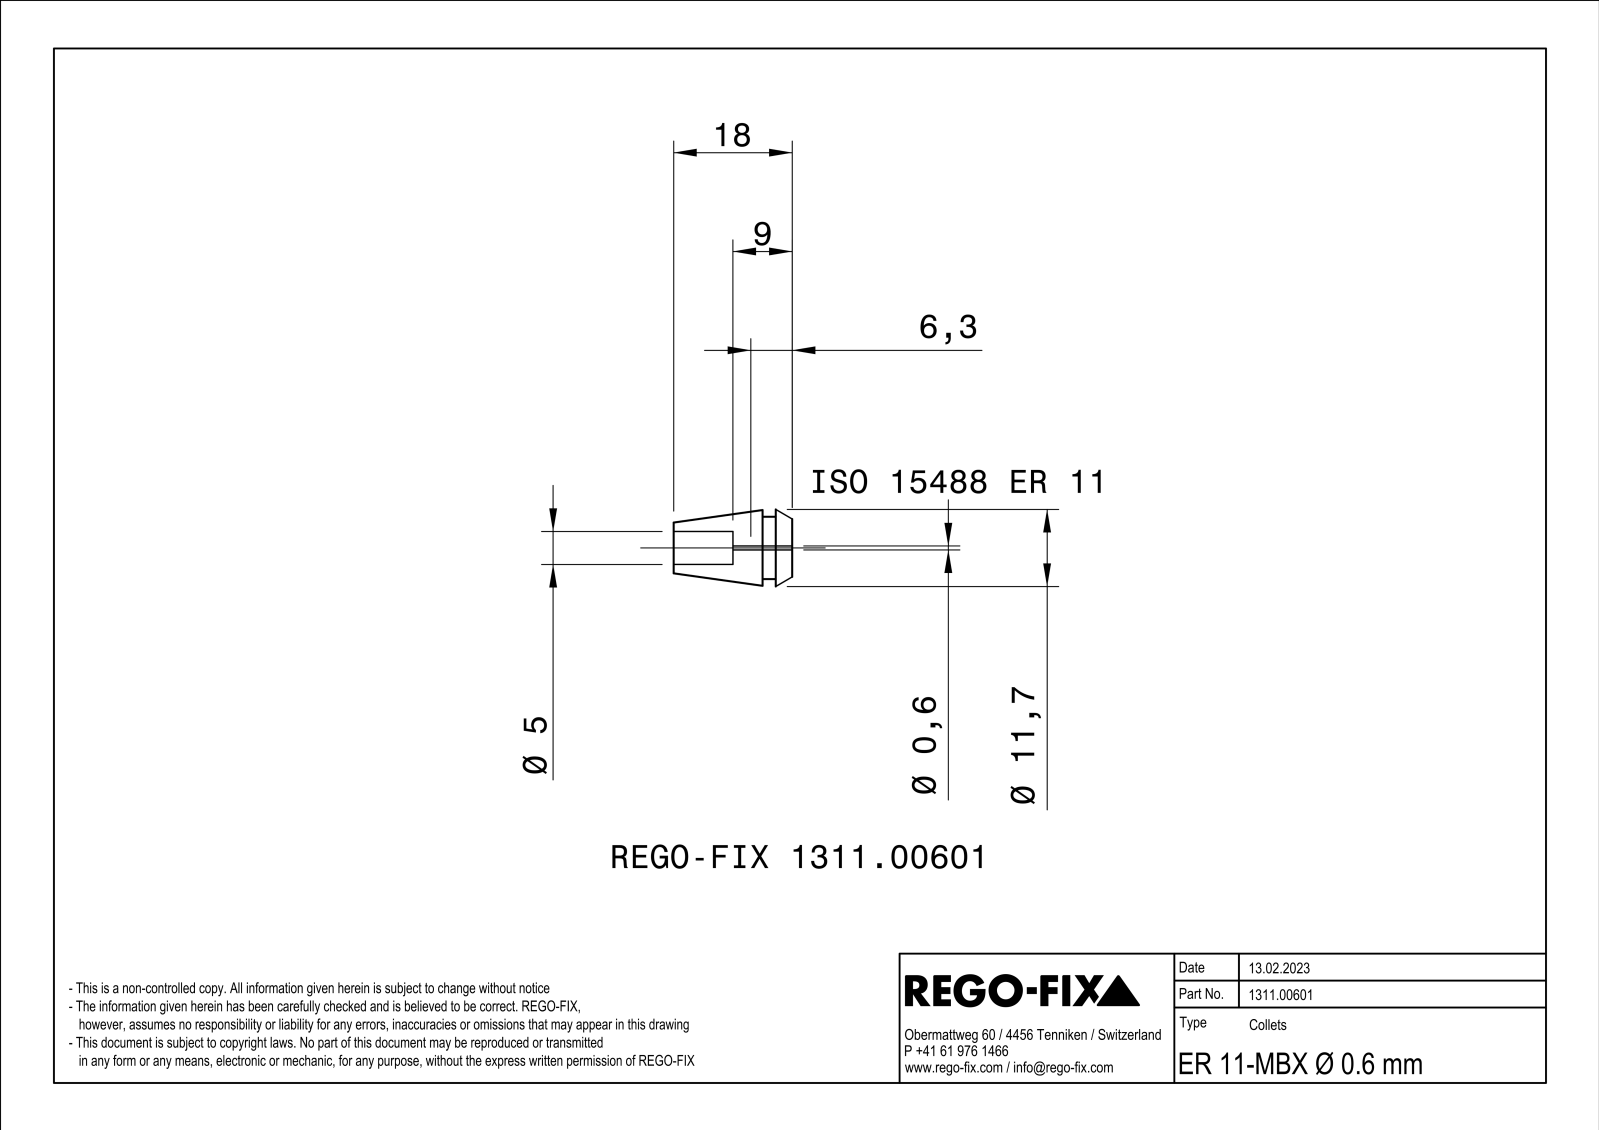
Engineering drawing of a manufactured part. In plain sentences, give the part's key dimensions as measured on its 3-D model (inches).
The part is named "NOCUT". Its 3-D file was written by "SIEMENS PLM Software Solid Edge ST10 (AUTOMOTIVE_DESIGN)". It is 1 solid with 91 faces: 26 planar, 19 cylindrical and 46 other. Overall it measures 0.709 by 0.449 by 0.448 inches. Its volume is 0.06 cubic inches and its surface area 1.947 square inches. Round holes: 3 of diameter 0.059, 1 of diameter 0.197. Round bosses or shafts: 1 of diameter 0.374. Partial cylindrical surfaces (rounded edges, fillets, slot ends): 3 of radius 0.984, 1 of radius 0.012. The main face-to-face distances are 0.031, 0.02, 0.177, 0.354, 0.709, 0.531, 0.098, 0.079, 0.61, 0.256. The hole center spacings are 0.067, 0.116.
